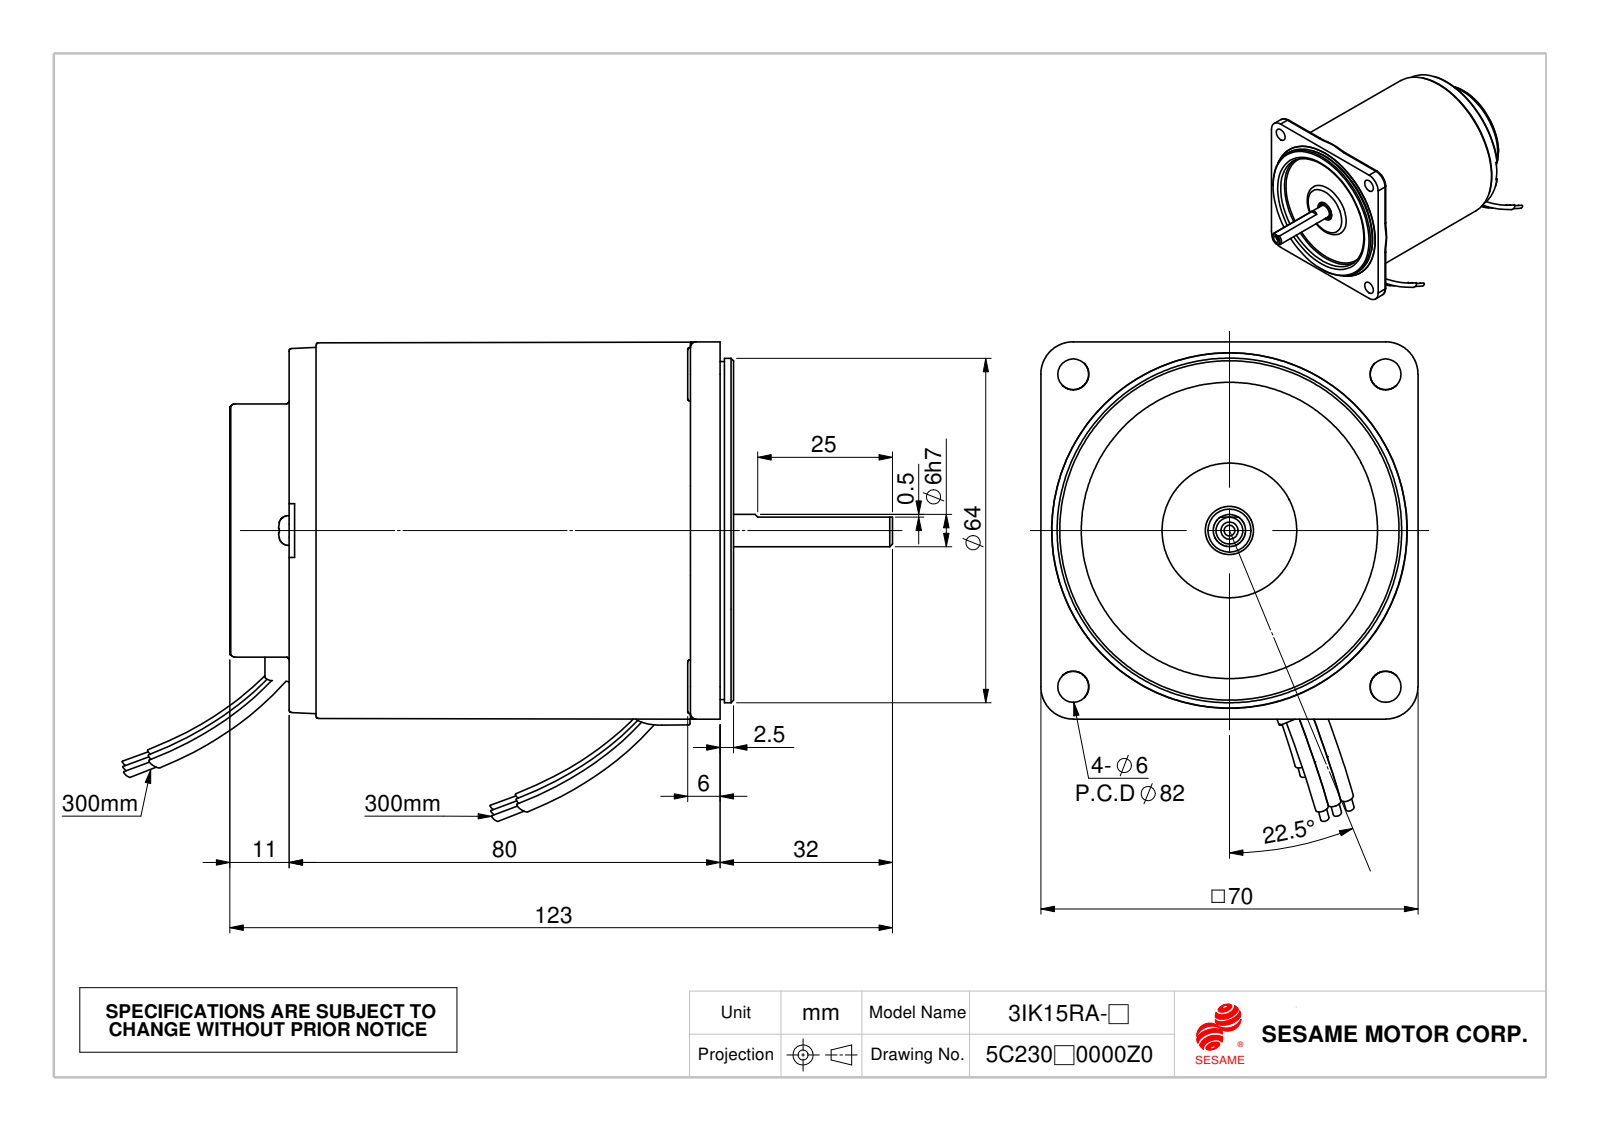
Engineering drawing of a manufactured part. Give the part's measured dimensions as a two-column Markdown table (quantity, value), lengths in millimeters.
| quantity | value |
| --- | --- |
| part name | M315_2車工; C364_車工(成品); 線扣; 15A_0.成品 |
| STEP written by | SolidWorks 2010 (CONFIG_CONTROL_DESIGN) |
| units | millimeters |
| bodies | 13 solids, 363 faces (128 planar, 106 cylindrical, 129 other) |
| overall size | 142.98 × 88.99 × 70 |
| volume | 334 579 mm³ |
| surface area | 47 359 mm² |
| round holes (diameter × count) | 5.75 × 4, 3.1 × 2, 2 × 1, 7.2 × 1, 9 × 1, 9.5 × 1, 18 × 1, 55 × 1, 60.5 × 1, 66 × 1 |
| round bosses / shafts (diameter × count) | 5.5 × 2, 3 × 2, 63.93 × 1, 62.73 × 1, 58 × 1, 57.42 × 1, 47 × 1, 46 × 1 |
| partial cylindrical surfaces (radius × count) | 1 × 10, 0.25 × 8, 0.3 × 8, 2.5 × 5, 6 × 4, 5.25 × 1, 33.87 × 1 |
| main face-to-face distances | 77.4, 77.5, 75.89, 1.51, 1.61, 1.5, 79, 3.11, 1.6, 12 |
| hole center spacings | 29.1, 41, 57.98, 62.61, 26.5, 82, 53 |
